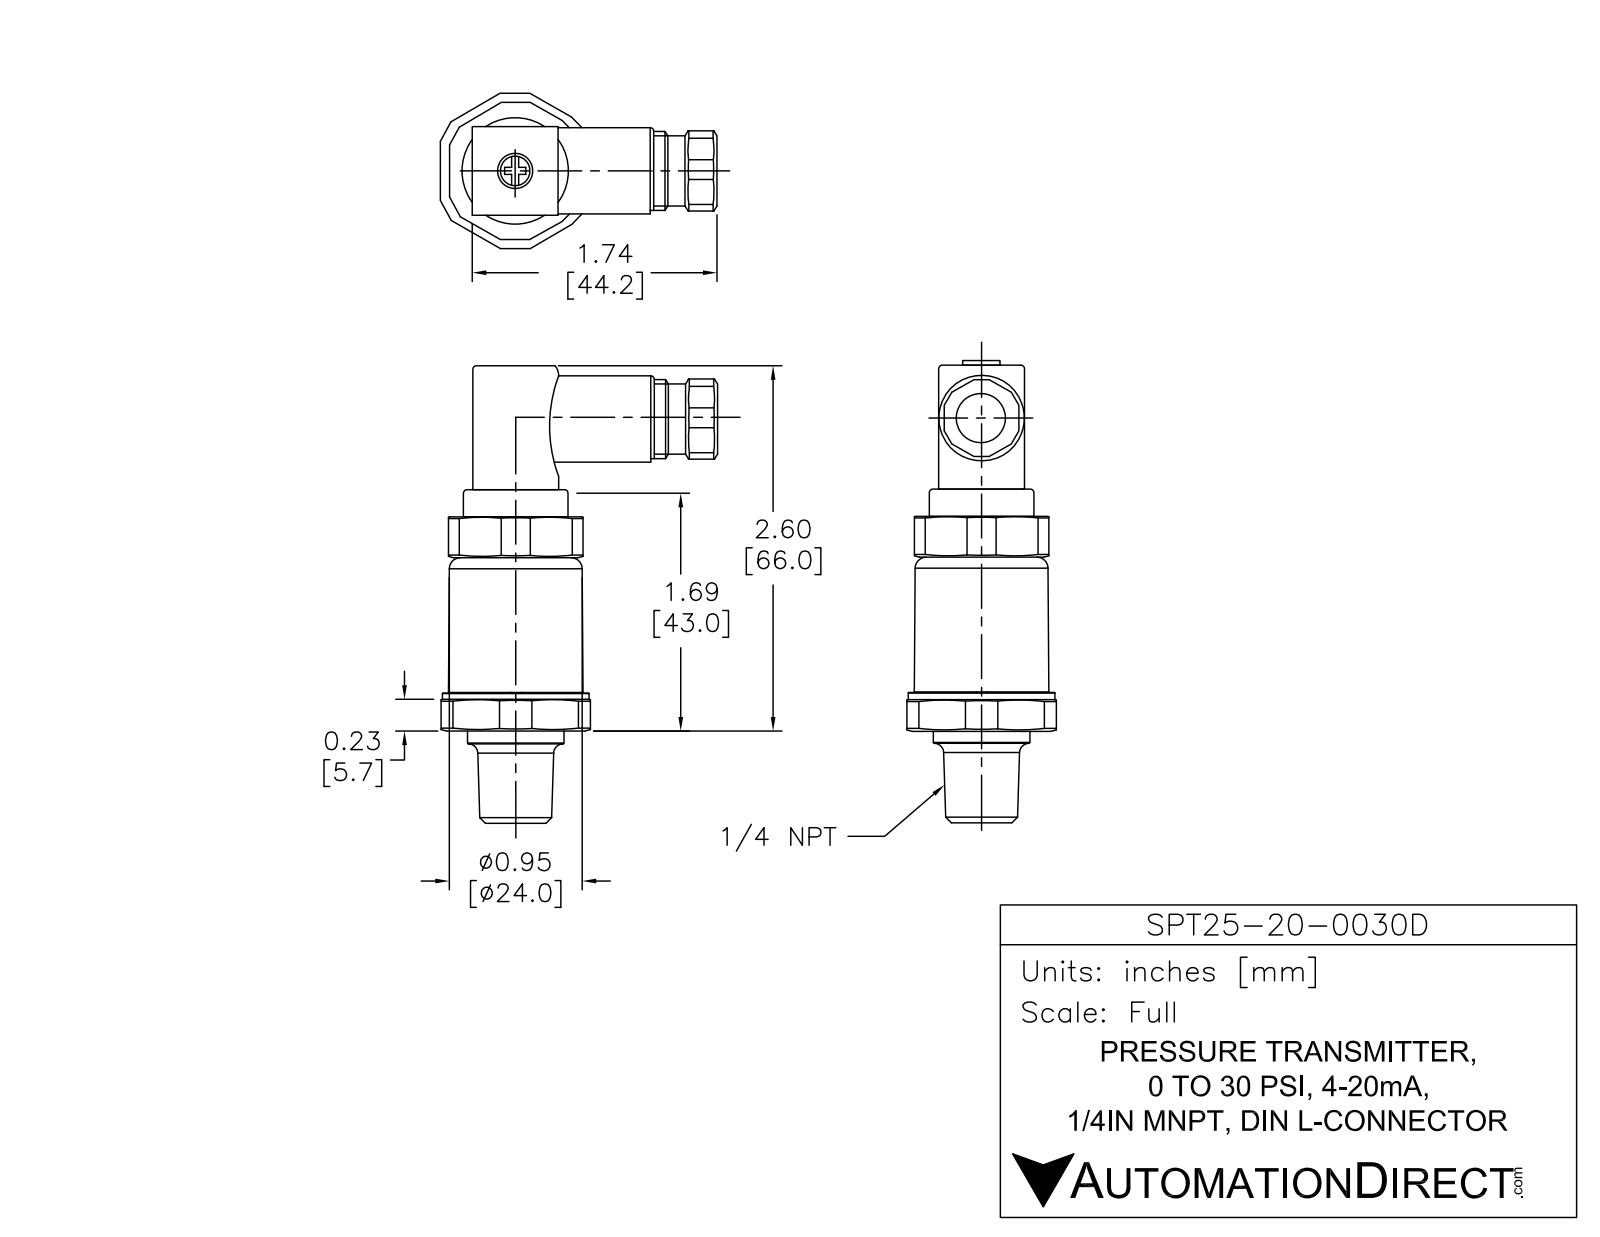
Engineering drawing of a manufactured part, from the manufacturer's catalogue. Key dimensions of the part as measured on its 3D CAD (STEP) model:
Part name (STEP PRODUCT): SPT25-20-0030D
STEP written by: SolidWorks 2011 (AUTOMOTIVE_DESIGN)
Units: millimetres
Bodies: 5 solids, 170 faces (96 planar, 64 cylindrical, 10 other)
Overall size (bounding box): 81.25 × 38.01 × 35.71
Volume: 27 900 mm³ · Surface area: 10 134 mm²
Round holes (diameter × count): ⌀1 ×1, ⌀3.3 ×1, ⌀7 ×1, ⌀8 ×1
Round bosses / shafts (diameter × count): ⌀26.75 ×1, ⌀24 ×1, ⌀17.5 ×1, ⌀15 ×1, ⌀14 ×1, ⌀11 ×1
Partial cylindrical surfaces — rounded edges, fillets, slot ends (radius × count): R1.5 ×8, R1.15 ×4, R2.25 ×4, R2 ×3, R1.15 ×1, R1.17 ×1, R14.5 ×1
Main face-to-face distances: 1.5, 29.5, 31, 15.75, 0.35, 15.4, 6.75, 37.75, 36.25, 5
Hole centre spacings: 1.33
